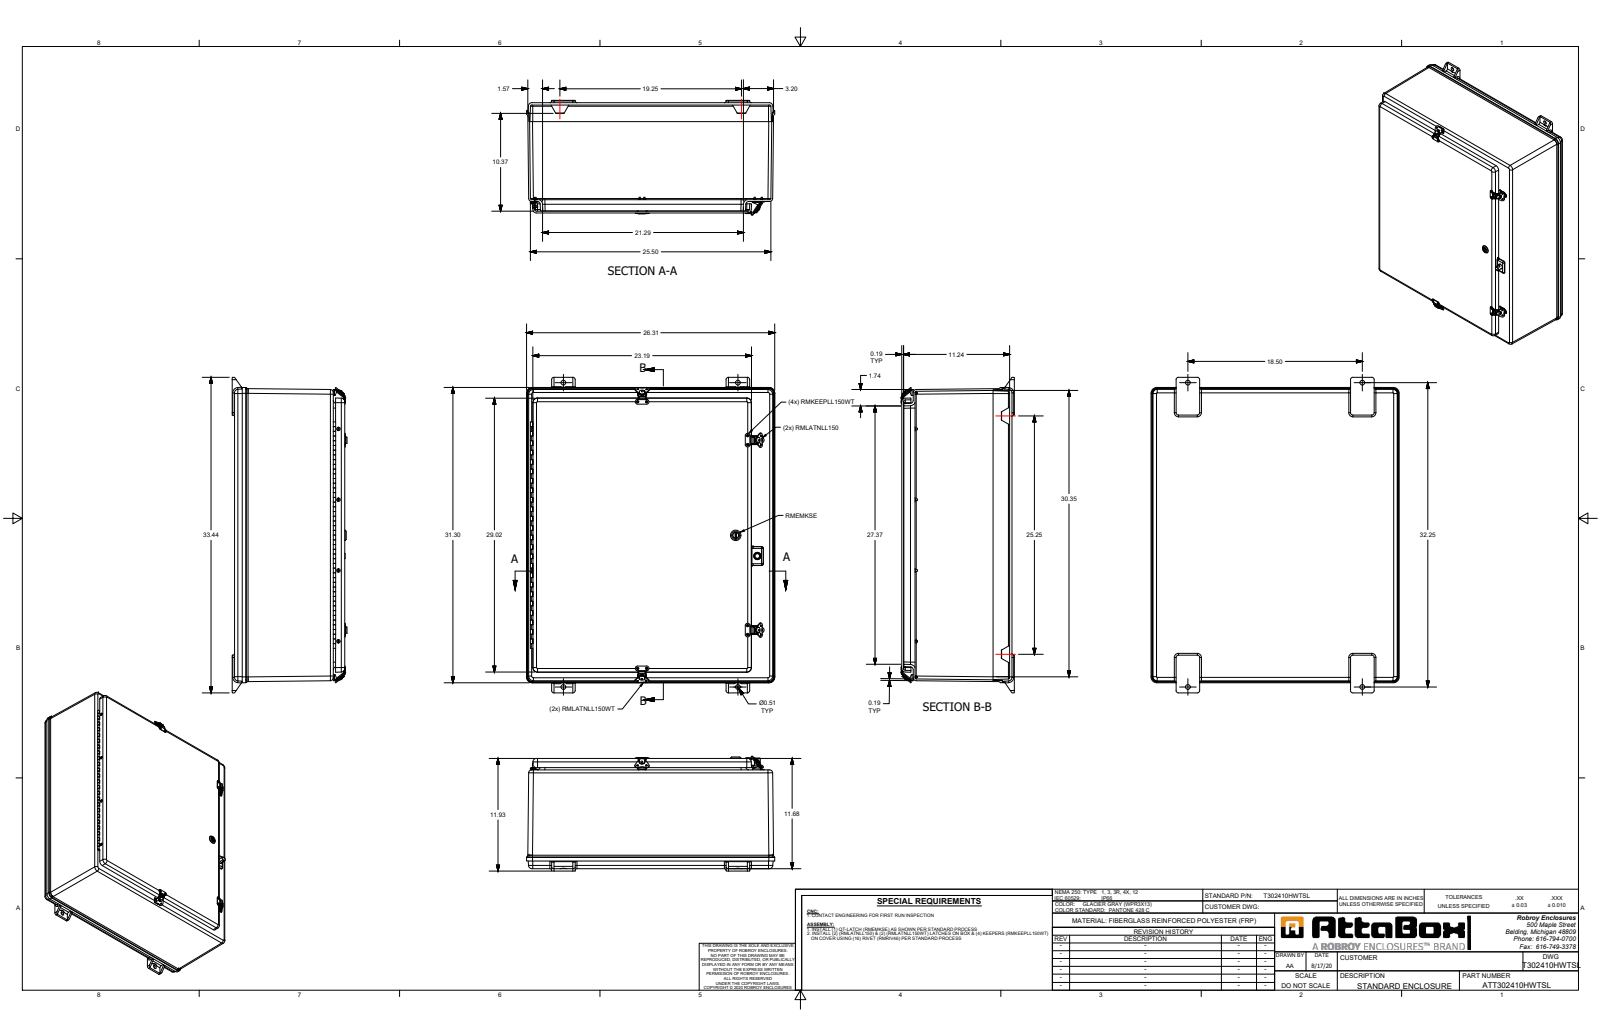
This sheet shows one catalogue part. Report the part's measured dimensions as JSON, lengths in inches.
{"part_name": "T302410HWTSL", "step_written_by": "SolidWorks 2019 (AUTOMOTIVE_DESIGN)", "units": "inches", "bodies": {"solids": 95, "faces": 2073, "planar": 947, "cylindrical": 845, "other": 281}, "overall_size": [33.438, 26.313, 12.174], "volume_in3": 643.2, "surface_area_in2": 6528, "round_holes": [[0.13, 24], [0.133, 12], [0.1, 10], [0.104, 8], [0.187, 8], [0.201, 8], [0.191, 6], [0.075, 5], [0.135, 4], [0.139, 4], [0.14, 4], [0.189, 4]], "round_bosses_or_shafts": [[0.125, 12], [0.357, 8], [0.283, 8], [0.187, 8], [0.14, 8], [0.66, 4], [0.582, 4], [0.525, 4]], "partial_cylinders_radius": [[0.25, 34], [0.015, 32], [0.012, 30], [0.06, 17], [0.011, 16], [0.02, 16], [0.07, 16], [0.079, 16]], "face_to_face_distances": [0.187, 0.25, 0.188, 11.682, 11.432, 11.494, 11.244, 10.281, 10.468, 10.031], "hole_center_spacings": [20.125, 7.5, 0.281, 15, 0.125, 0.125, 0.157, 0.619]}
